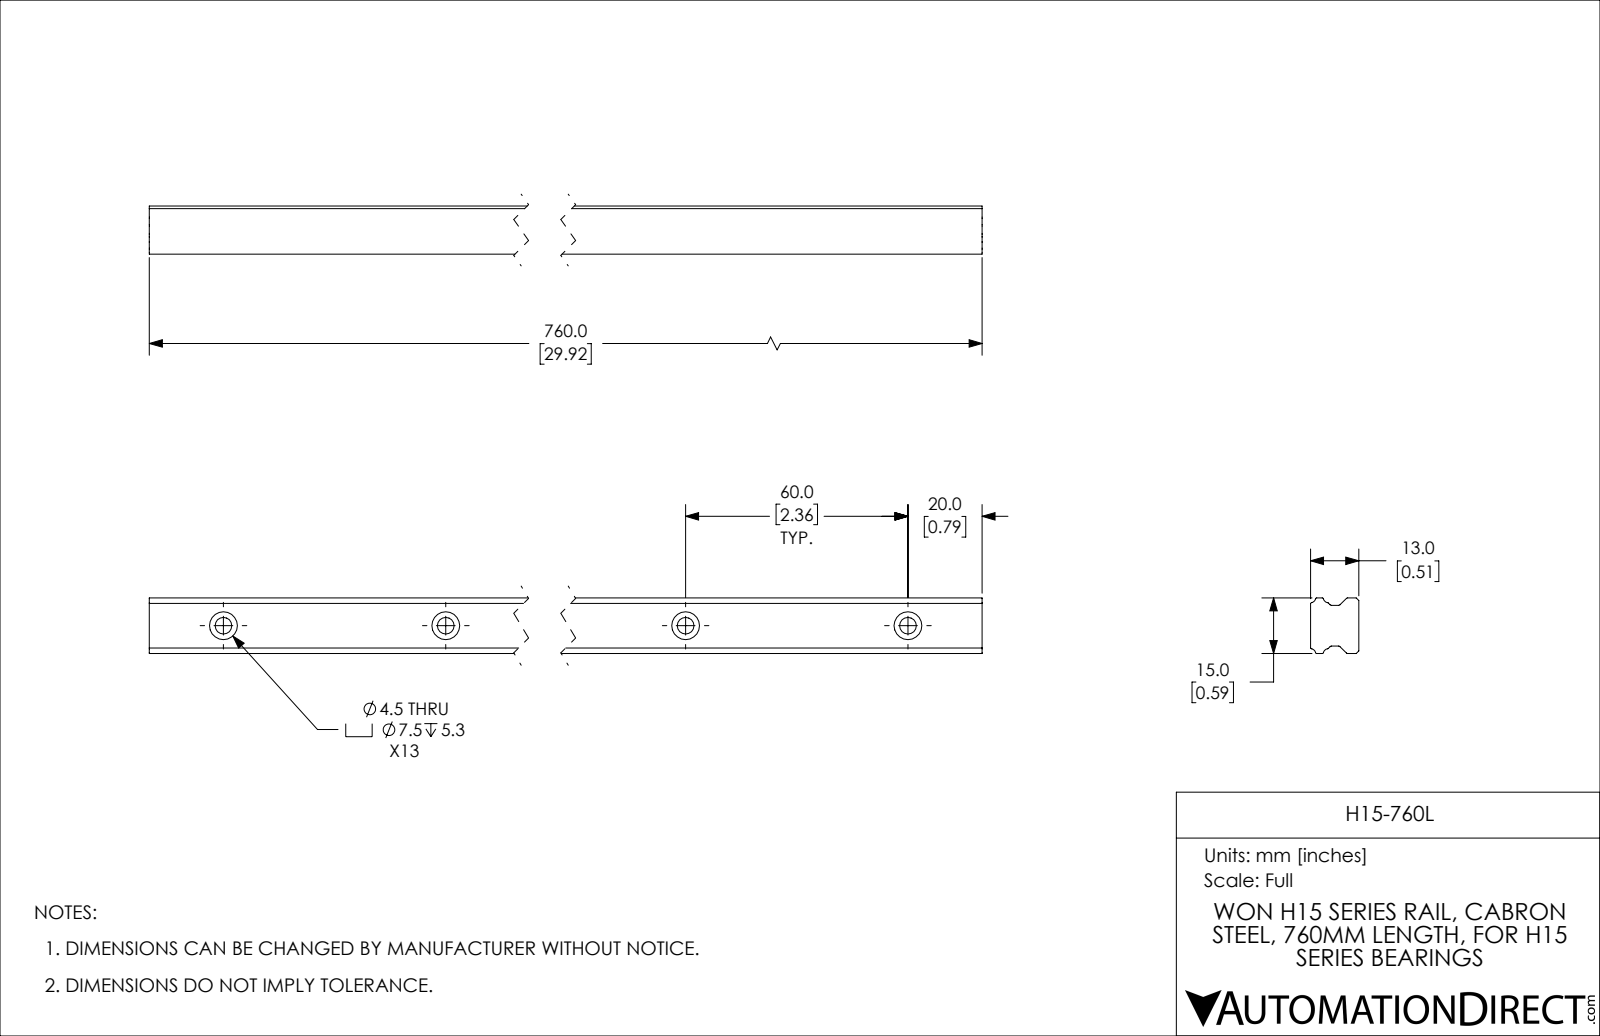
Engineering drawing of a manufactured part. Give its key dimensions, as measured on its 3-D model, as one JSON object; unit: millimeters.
{"part_name": "H15-760L", "step_written_by": "SolidWorks 2019 (CONFIG_CONTROL_DESIGN)", "units": "millimeters", "bodies": {"solids": 1, "faces": 99, "planar": 29, "cylindrical": 70, "other": 0}, "overall_size": [760, 15, 13], "volume_mm3": 127035, "surface_area_mm2": 46212, "round_holes": [[4.5, 13], [7.5, 13]], "partial_cylinders_radius": [[0.3, 6], [0.5, 6], [1.4, 4], [0.6, 2]], "face_to_face_distances": [13, 2, 15, 11, 12.37, 6.08, 6.29, 7.7, 5.3, 760], "hole_center_spacings": [60, 120, 180, 240, 300, 360, 420, 480]}
